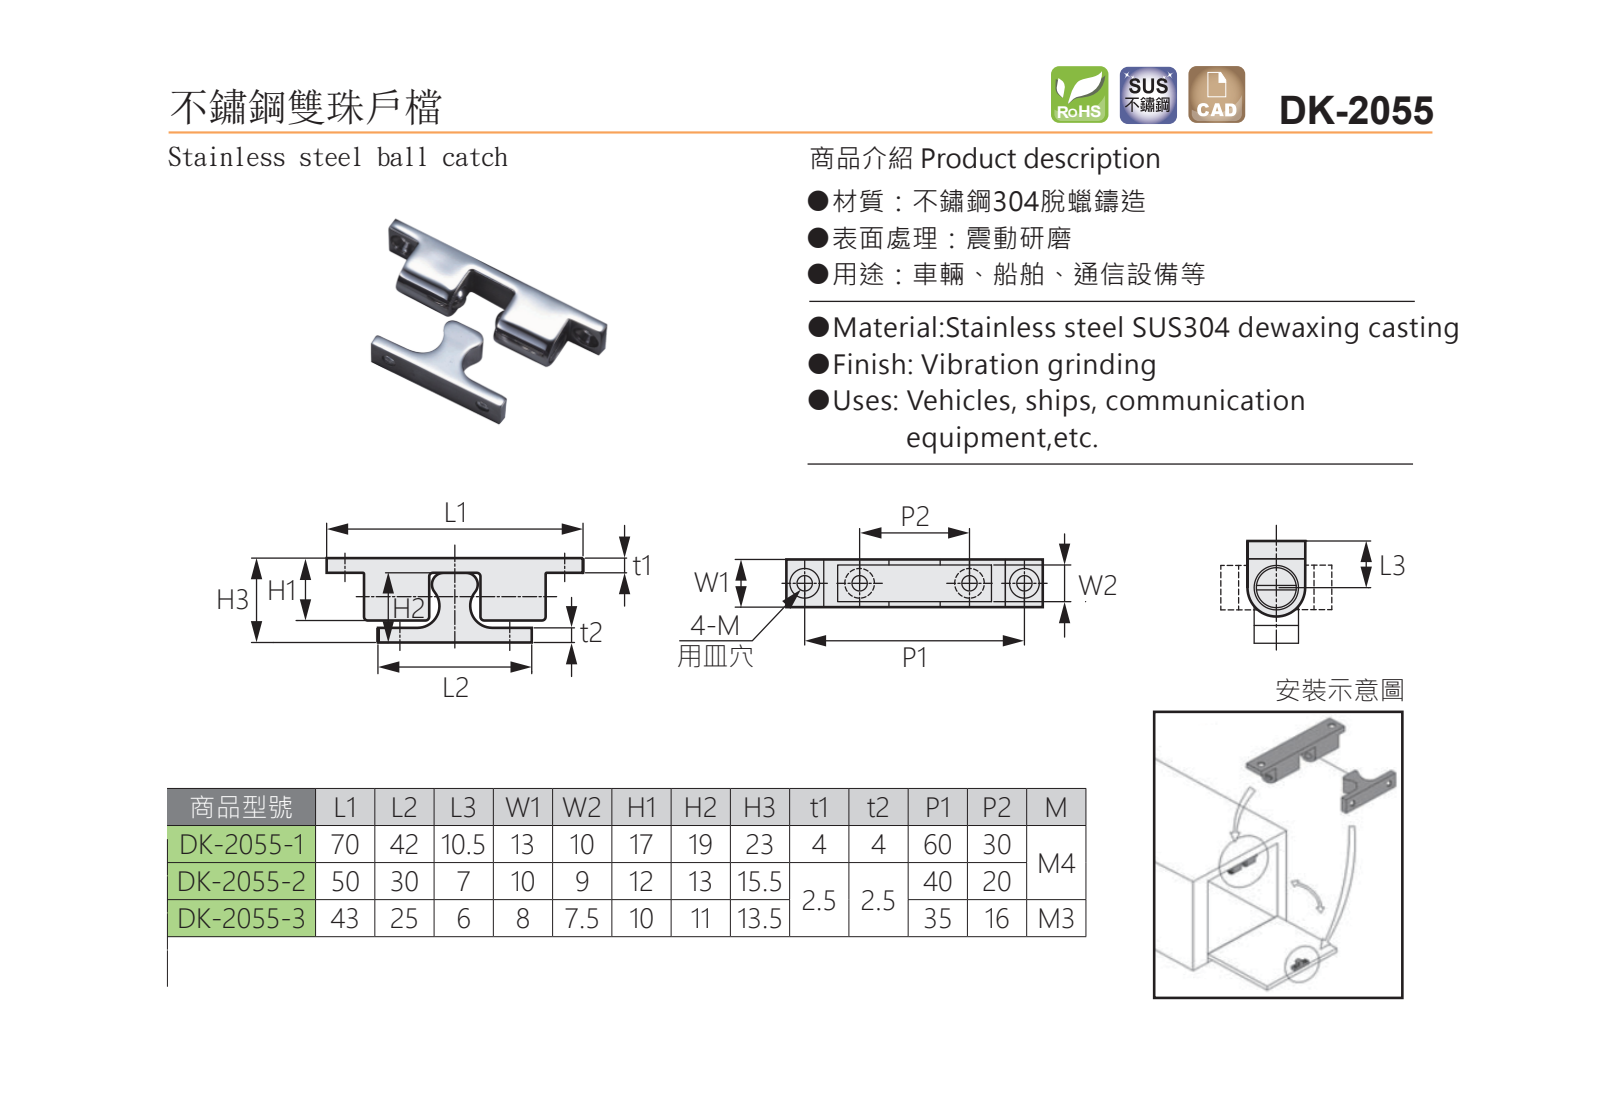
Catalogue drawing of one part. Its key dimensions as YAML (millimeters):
part_name: "鋼珠; TKS-2055-1; 母邊; 公邊 (+1 more)"
step_written_by: "SolidWorks 2010 (CONFIG_CONTROL_DESIGN)"
units: millimeters
bodies: {solids: 6, faces: 318, planar: 38, cylindrical: 108, other: 172}
overall_size: [70.7, 22.6, 13]
volume: 10576
surface_area: 7319
round_holes:
  - {diameter: 4.3, count: 4}
  - {diameter: 8.2, count: 4}
  - {diameter: 7.5, count: 1}
  - {diameter: 9.1, count: 1}
partial_cylinders:
  - {radius: 0.2, count: 38}
  - {radius: 1.5, count: 16}
  - {radius: 4, count: 2}
  - {radius: 5, count: 2}
  - {radius: 6, count: 2}
  - {radius: 10, count: 2}
  - {radius: 6.5, count: 1}
face_to_face_distances: [1.5, 11.5, 13, 22.6, 3.8, 18.8, 10, 48.3, 32.3, 16]
hole_center_spacings: [15.25, 45.25, 30, 60.5]
